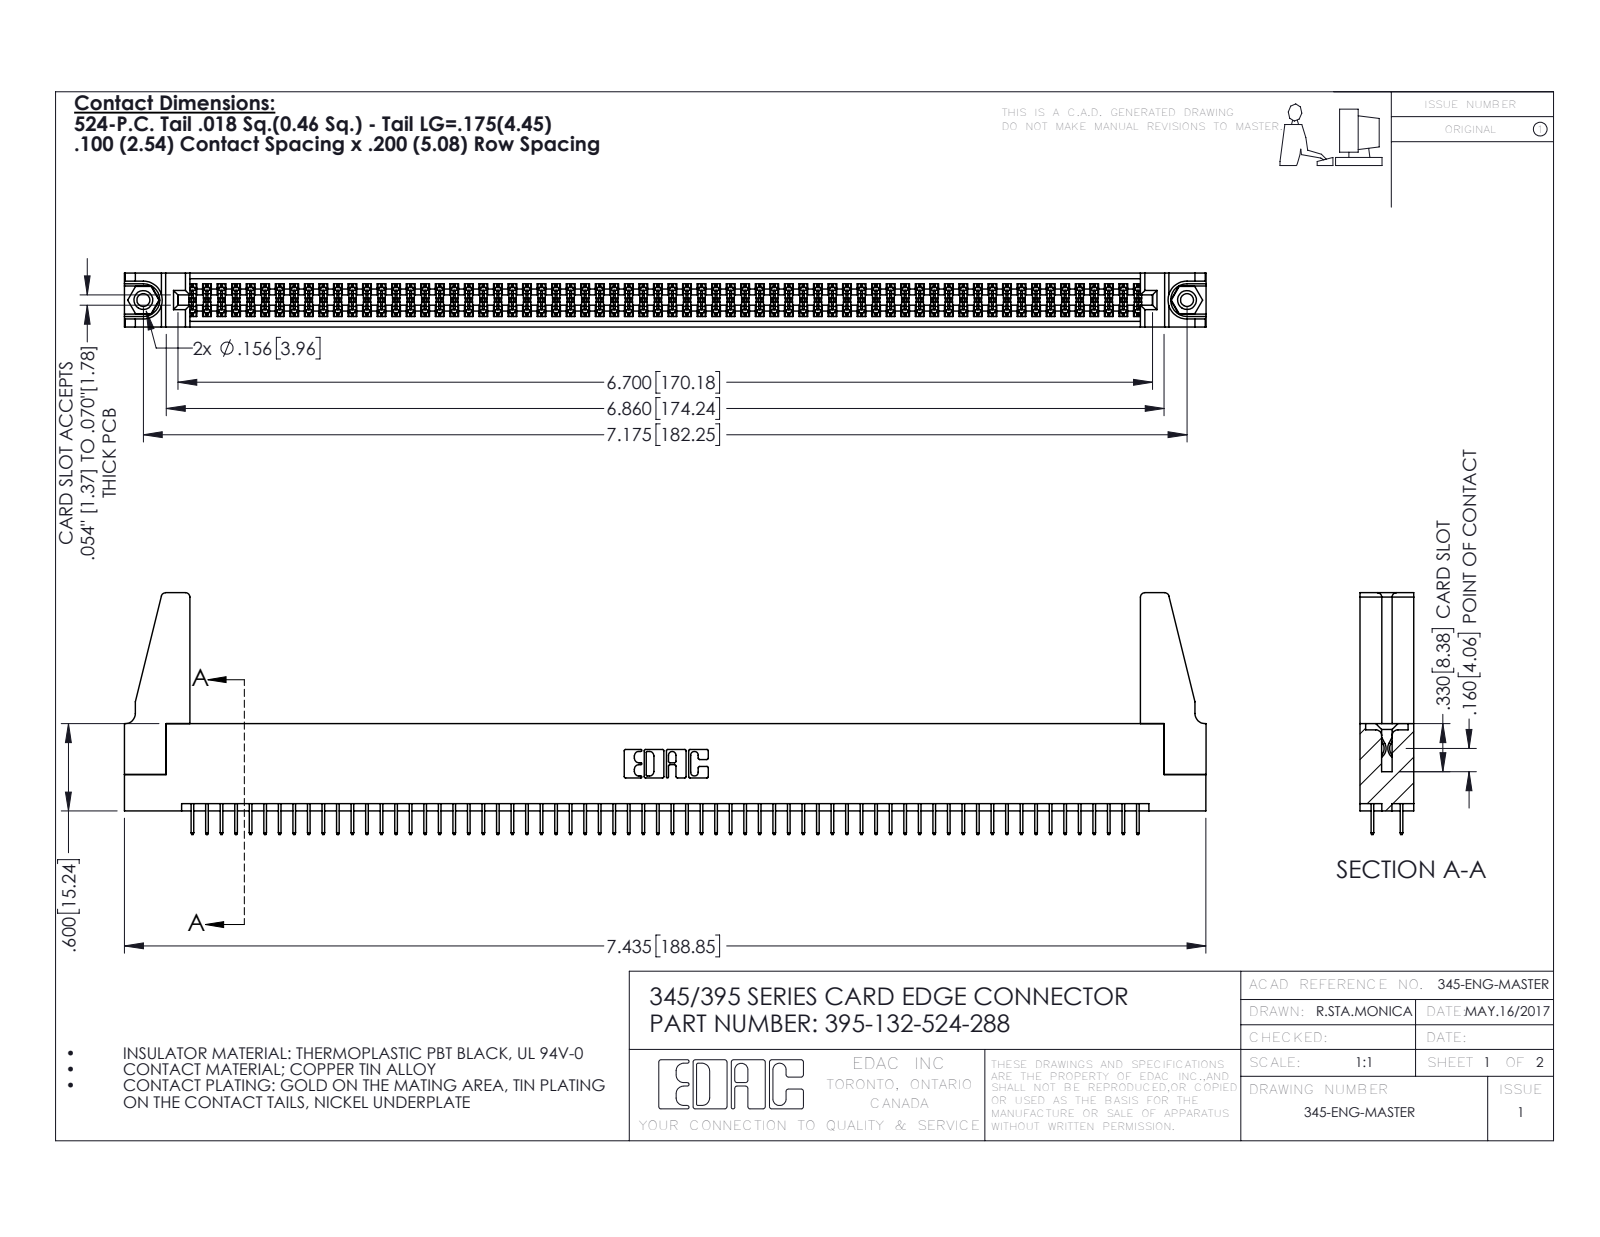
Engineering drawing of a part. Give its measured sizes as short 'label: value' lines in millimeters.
name: 345-250-001_345-250-001-102; 395-132-524-288; 345-220-078_345-220-088; 345 Part_Flush Mounting Lugs - 0.156 Dia-TH (+1 more)
written by: SolidWorks 2016 (CONFIG_CONTROL_DESIGN)
unit: mm
bodies: 137 solids, 7378 faces (5300 planar, 2062 cylindrical, 16 other)
size: 188.9 × 42.2 × 9.4
volume: 21 630 mm³; area: 30 210 mm²
holes: 2× ⌀2.3, 2× ⌀3.2, 2× ⌀4, 1× ⌀1.6
bosses: 2× ⌀3.9
rounds: 198× R0.2, 22× R0.3, 8× R0.8, 6× R0.2, 6× R0.8, 3× R0.7, 2× R0.4, 2× R0.5
face distances: 1.8, 7.6, 9.4, 5.1, 2.5, 6.9, 0.6, 5.7, 1.8, 4.4
hole spacings: 6.9, 176.3, 182.2
